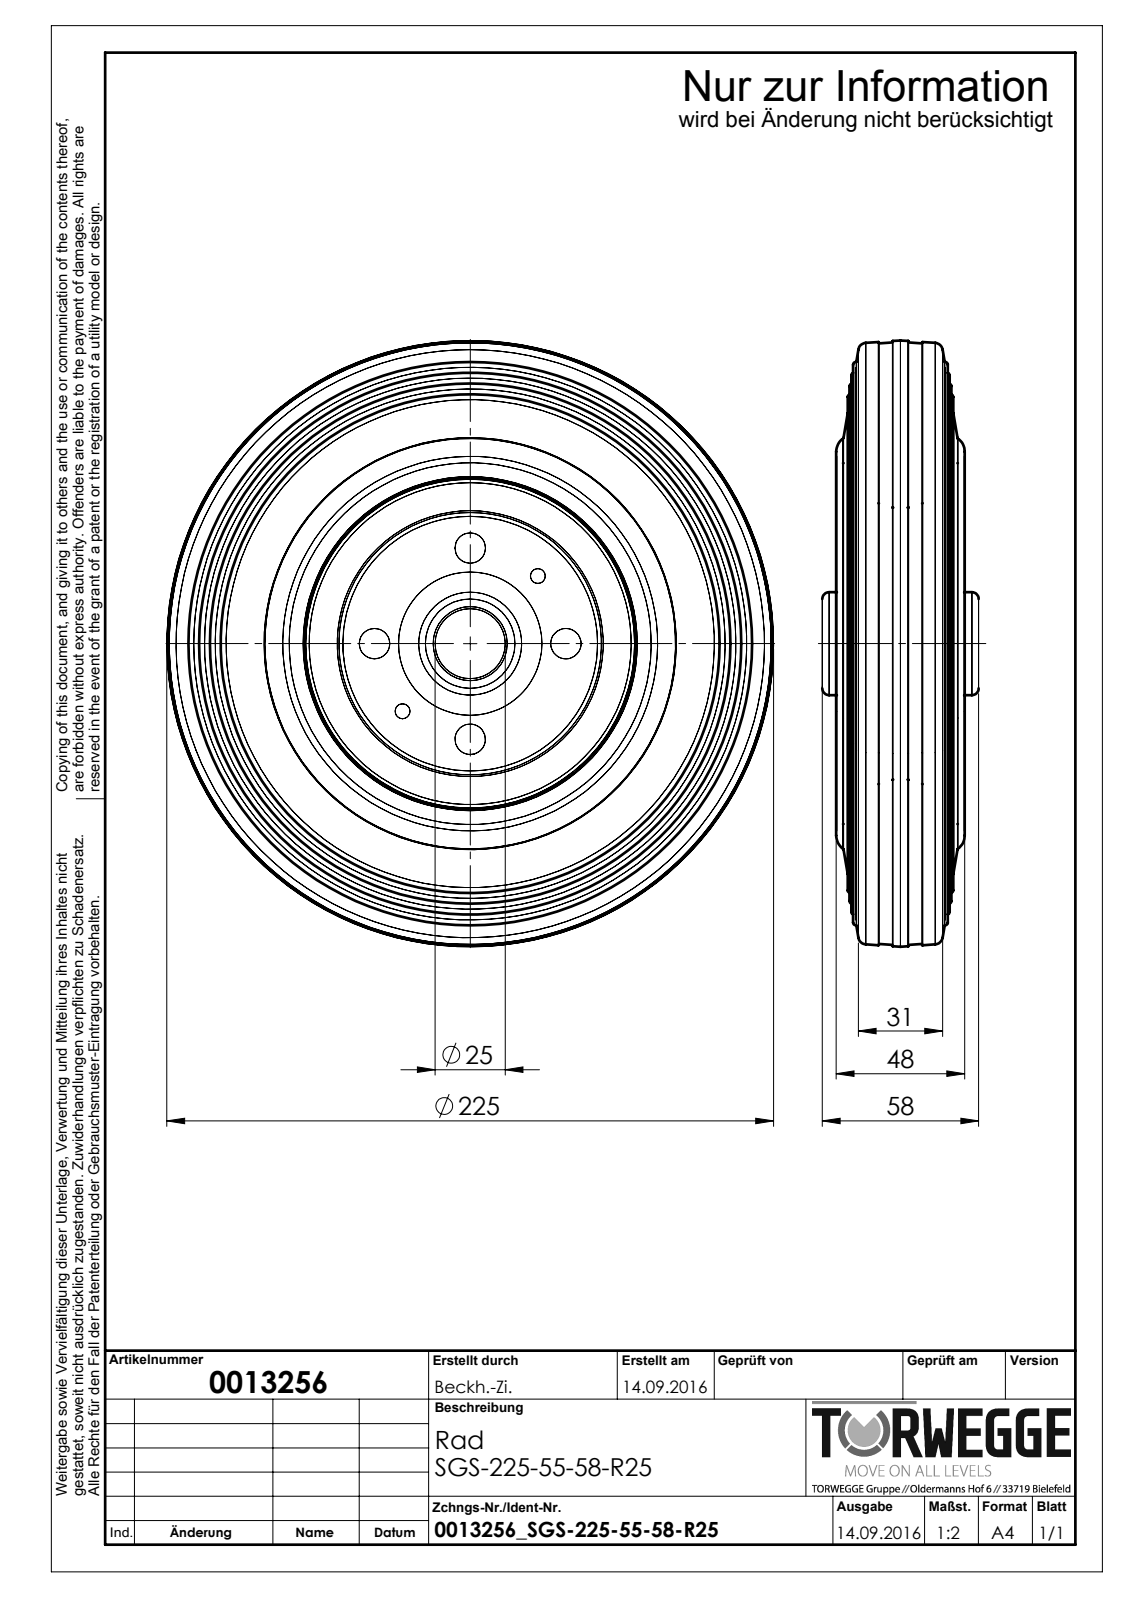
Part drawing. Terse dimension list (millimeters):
name: 0013256_SGS-225-55-58-R25_neu
written by: SolidWorks 2016 (AUTOMOTIVE_DESIGN)
unit: mm
bodies: 0 solids, 264 faces (30 planar, 70 cylindrical, 164 other)
size: 225.11 × 225.11 × 58
bosses: 4× ⌀11.3, 4× ⌀9.3, 4× ⌀8.5, 2× ⌀5.5, 1× ⌀134, 1× ⌀102.82, 1× ⌀38.2, 1× ⌀35.2
face distances: 1.5, 3, 27.5, 29, 7.05, 49.45, 20.45, 21.95, 26, 30.5
